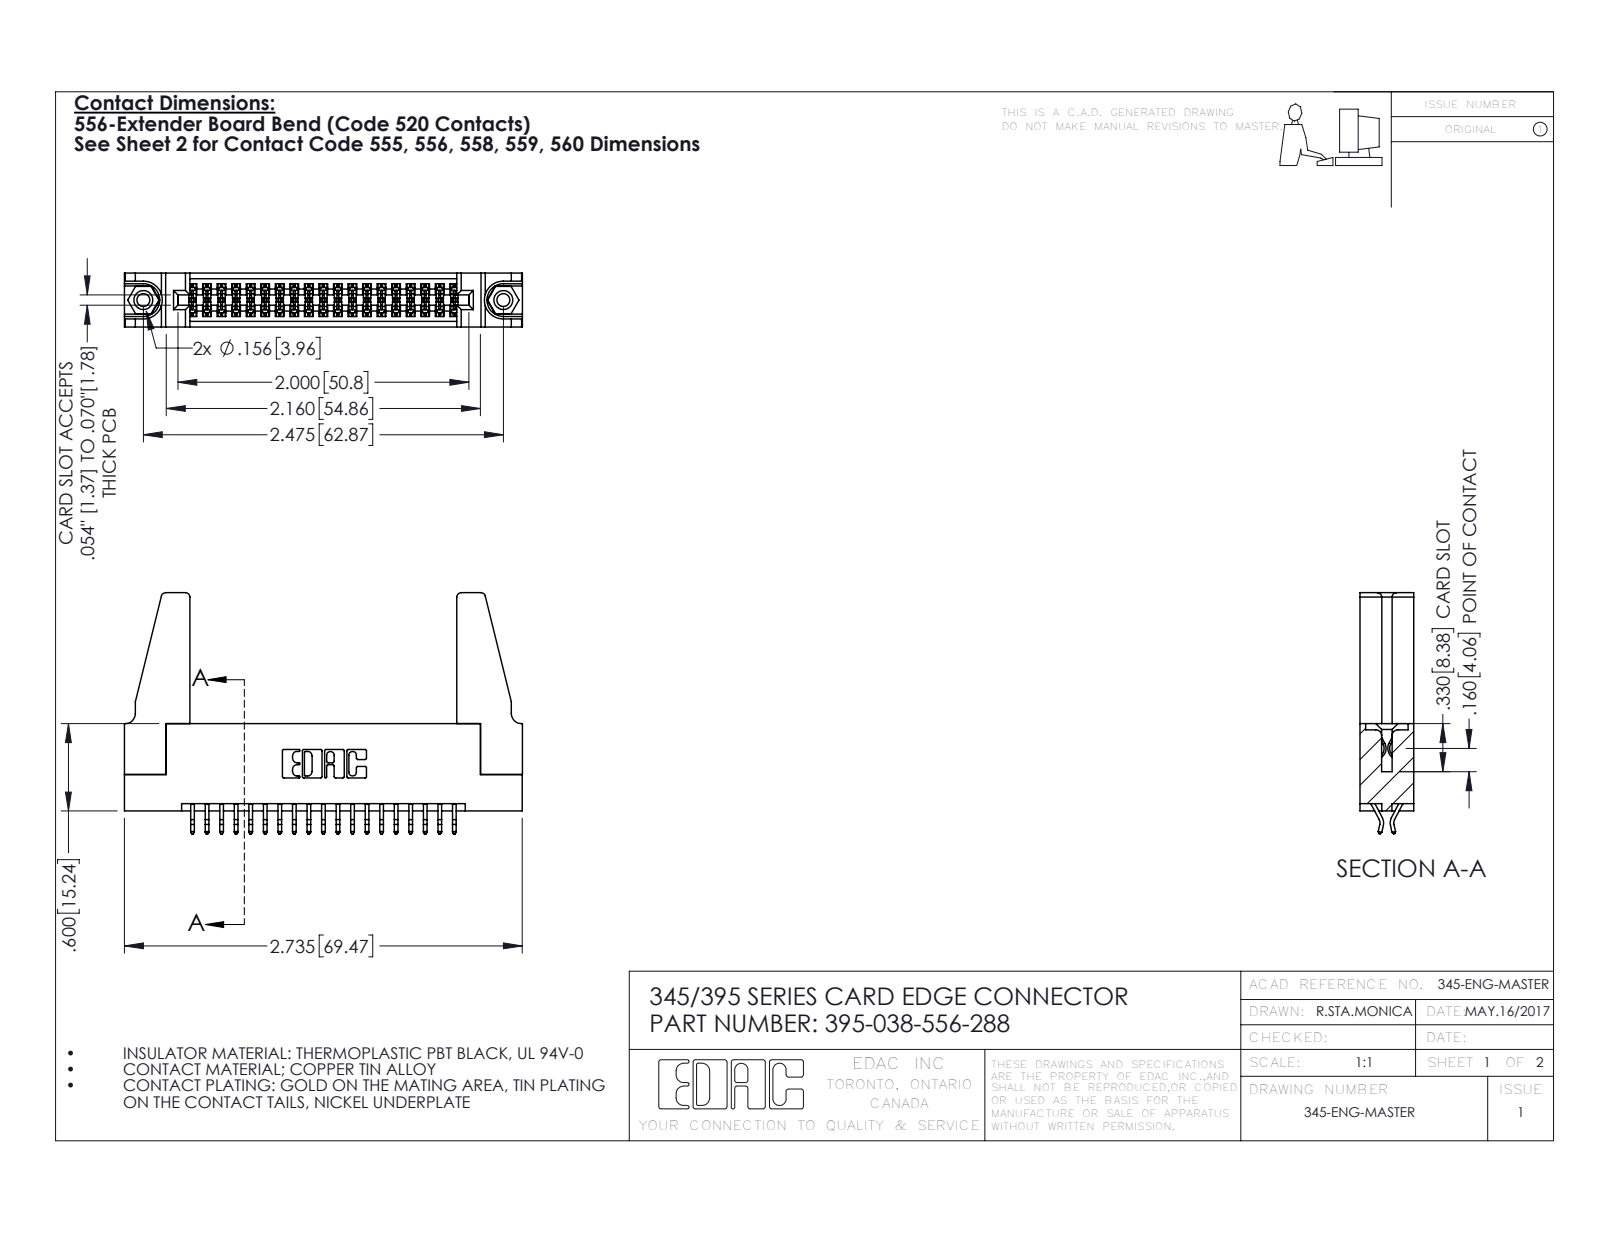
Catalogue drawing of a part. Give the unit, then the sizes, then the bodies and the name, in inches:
Units: inches
Overall size (bounding box): 2.736 × 1.657 × 0.37
Round holes (diameter × count): ⌀0.089 ×2, ⌀0.125 ×2, ⌀0.156 ×2, ⌀0.064 ×1
Round bosses / shafts (diameter × count): ⌀0.155 ×2
Partial cylindrical surfaces — rounded edges, fillets, slot ends (radius × count): R0.006 ×57, R0.01 ×22, R0.03 ×8, R0.007 ×6, R0.031 ×6, R0.026 ×3, R0.01 ×2, R0.014 ×2
Main face-to-face distances: 0.37, 0.072, 0.298, 0.2, 0.025, 0.098, 0.272, 0.225, 0.175, 0.148
Hole centre spacings: 0.27, 2.241, 2.475
Volume: 0.597 in³ · Surface area: 19.07 in²
Bodies: 43 solids, 2378 faces (1558 planar, 804 cylindrical, 16 other)
Part name (STEP PRODUCT): 345-220-078_345-220-088; 345 Part_Flush Mounting Lugs - 0.156 Dia-TH; 395-038-556-288; 345-292-001_556 Tail (+1 more)
STEP written by: SolidWorks 2016 (CONFIG_CONTROL_DESIGN)
